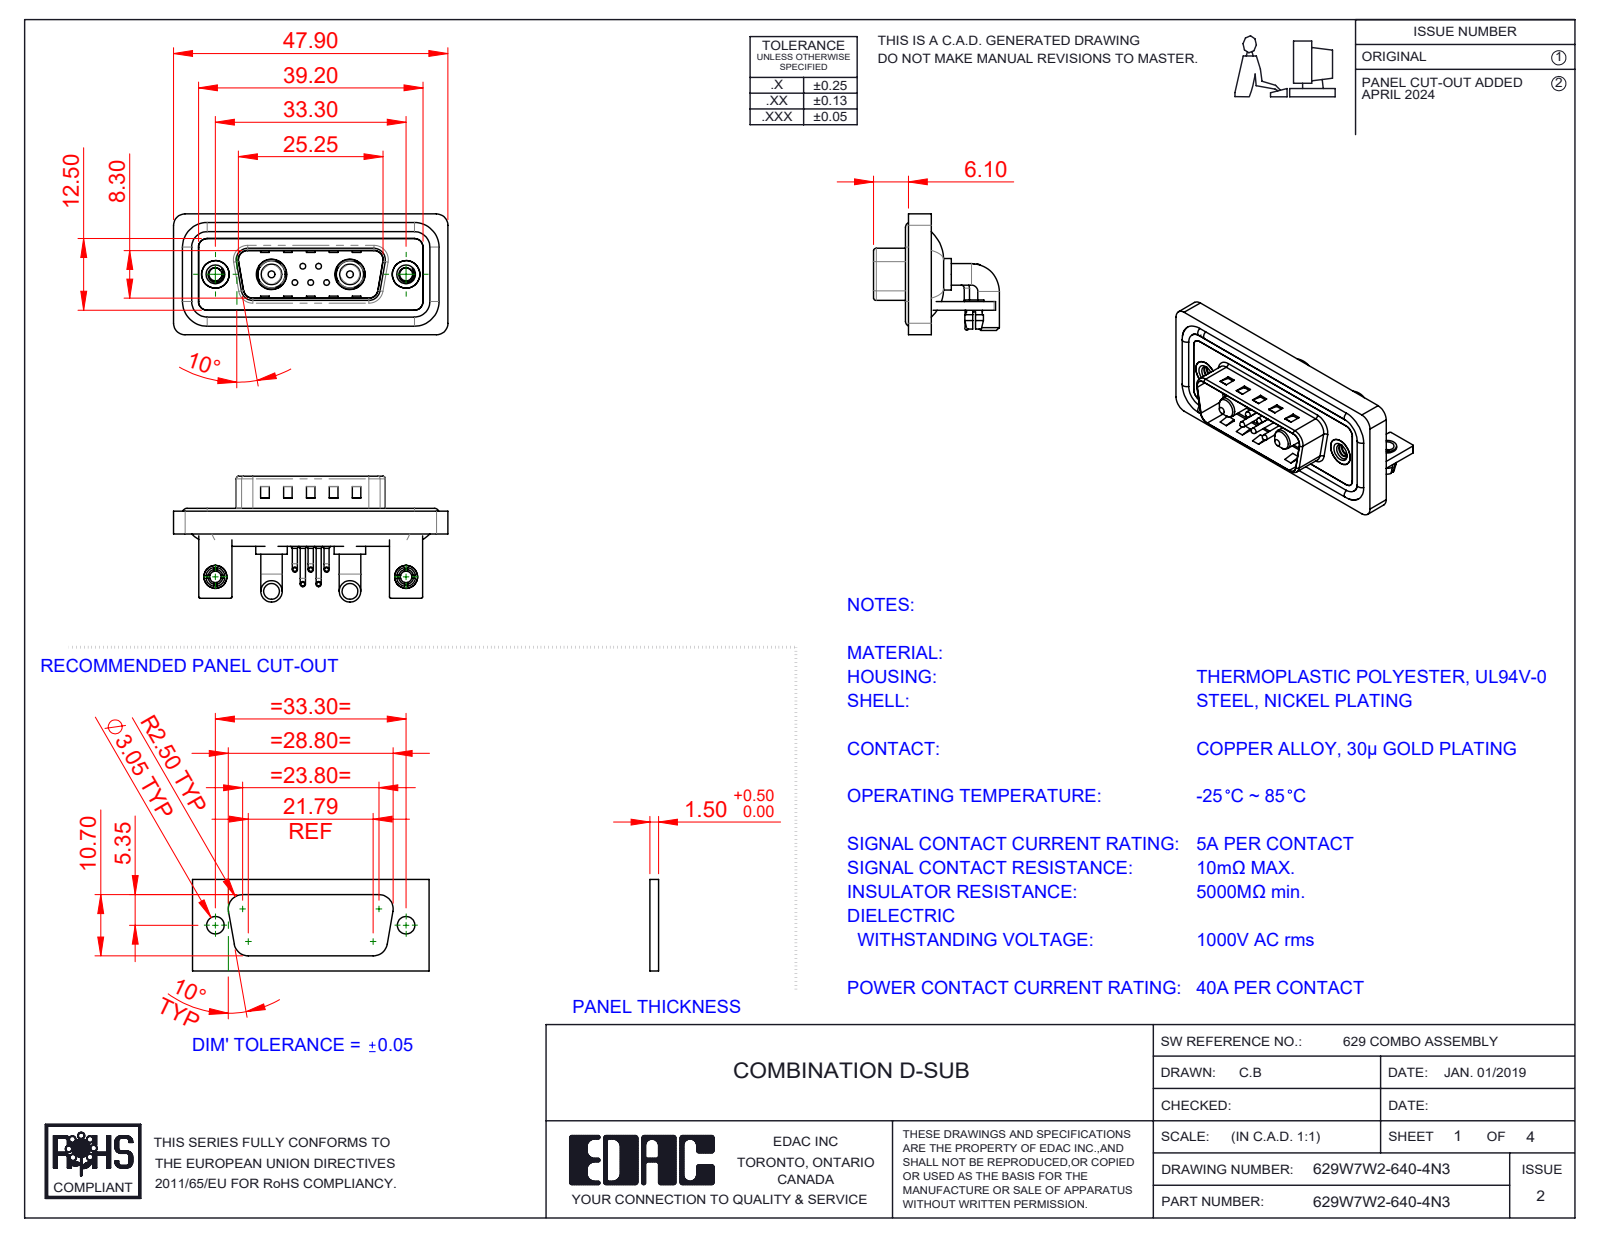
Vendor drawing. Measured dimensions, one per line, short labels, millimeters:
name: 629Combo Shell Front_15 Contacts; 629Combo Threaded Rivet_3; 629Combo Shell Rear_15 Contacts; 629Combo Contact Row 1 (+7 more)
written by: SolidWorks 2023 (CONFIG_CONTROL_DESIGN)
unit: mm
bodies: 20 solids, 1215 faces (585 planar, 456 cylindrical, 174 other)
size: 47.9 × 21.98 × 21.1
volume: 6 140 mm³; area: 10 026 mm²
holes: 7× ⌀2, 5× ⌀0.75, 5× ⌀1.6, 2× ⌀2.26, 2× ⌀2.5, 2× ⌀3.2, 2× ⌀4, 2× ⌀4.8, 2× ⌀4.85, 2× ⌀5, 2× ⌀5.3
bosses: 10× ⌀0.9, 5× ⌀1.5, 5× ⌀1, 5× ⌀0.65, 4× ⌀3.75, 4× ⌀1.6, 2× ⌀5.5, 2× ⌀5.2
rounds: 21× R2, 18× R1.5, 16× R0.25, 9× R0.5, 8× R1.6, 5× R1.01, 4× R0.6, 4× R0.65
face distances: 0.4, 0.8, 1.5, 2.9, 2.1, 1.1, 1.6, 1.2, 3.7, 4.5
hole spacings: 3.16, 2.77, 9.8, 23.5, 33.3, 4.31, 4.33, 5.03
